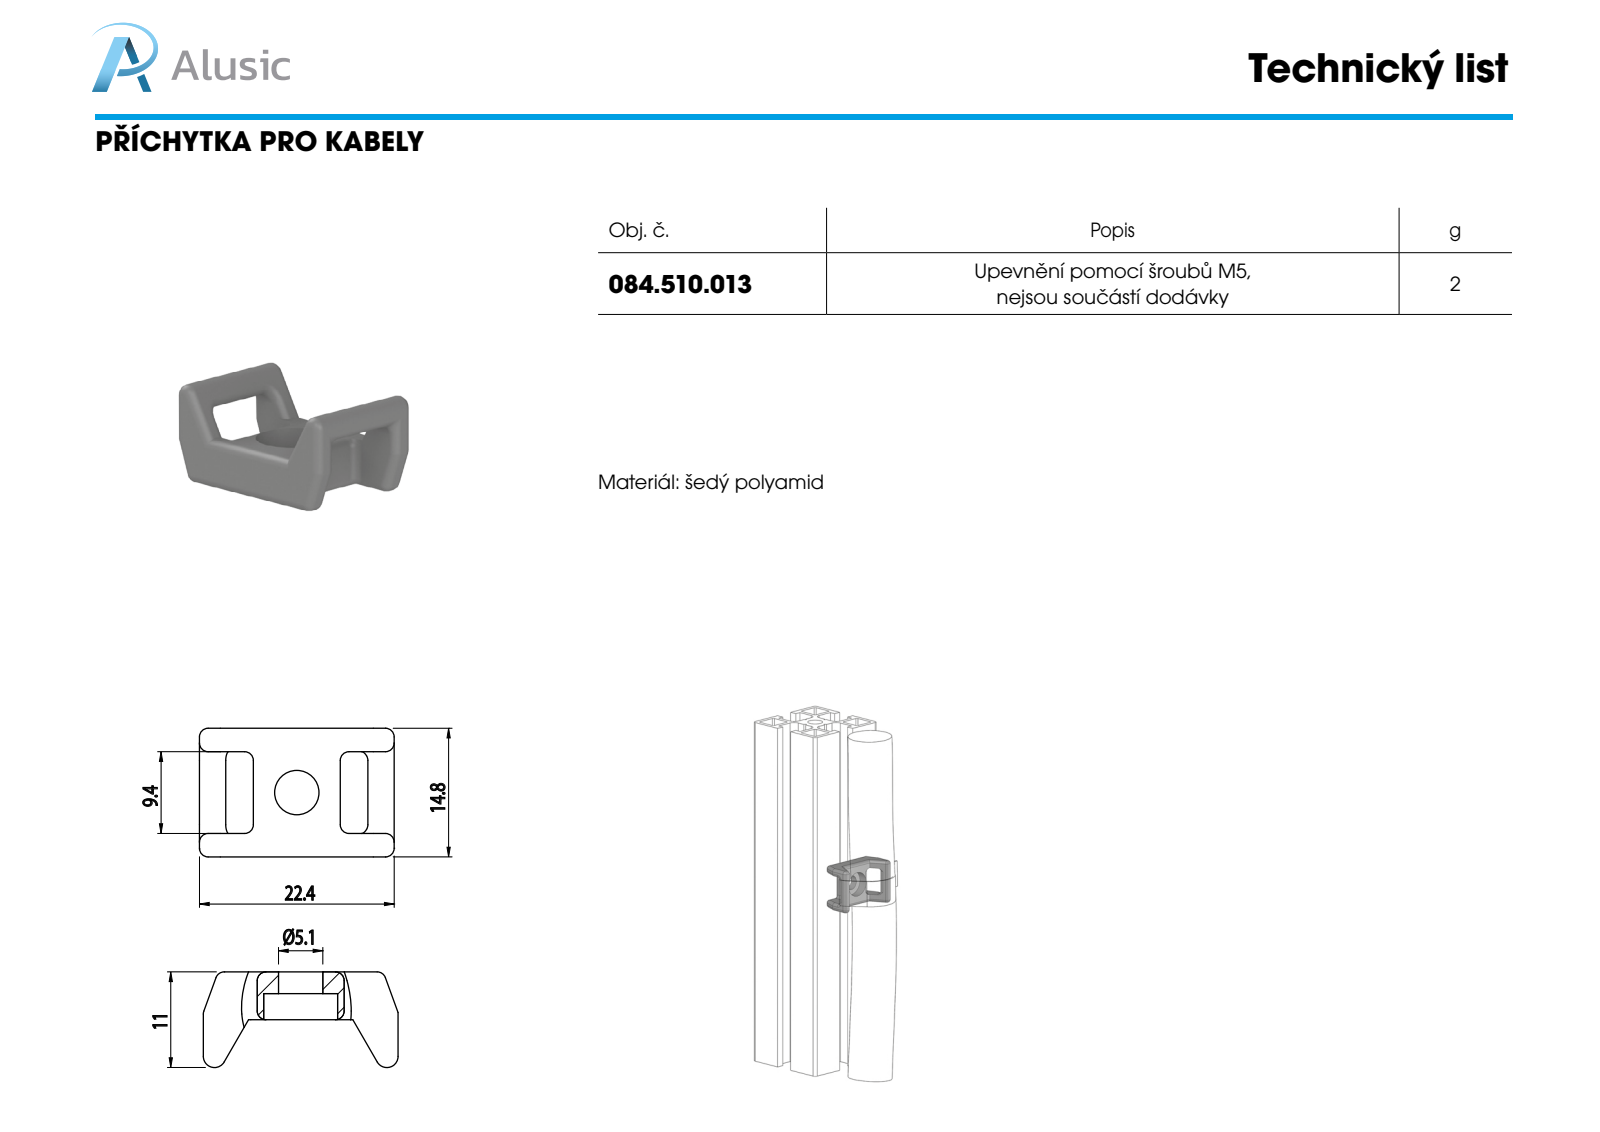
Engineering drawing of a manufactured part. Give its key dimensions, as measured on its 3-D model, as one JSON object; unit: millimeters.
{"part_name": "084.510.013", "step_written_by": "SolidWorks 2012 (CONFIG_CONTROL_DESIGN)", "units": "millimeters", "bodies": {"solids": 1, "faces": 115, "planar": 22, "cylindrical": 60, "other": 33}, "overall_size": [22.4, 14.8, 11], "volume_mm3": 1223, "surface_area_mm2": 1290, "round_holes": [[5.1, 1], [8.5, 1]], "partial_cylinders_radius": [[1, 46], [1.28, 2]], "face_to_face_distances": [14.8, 2.7, 12.1, 5.5, 2.5, 9.4, 3, 6.2, 16.2, 10]}
